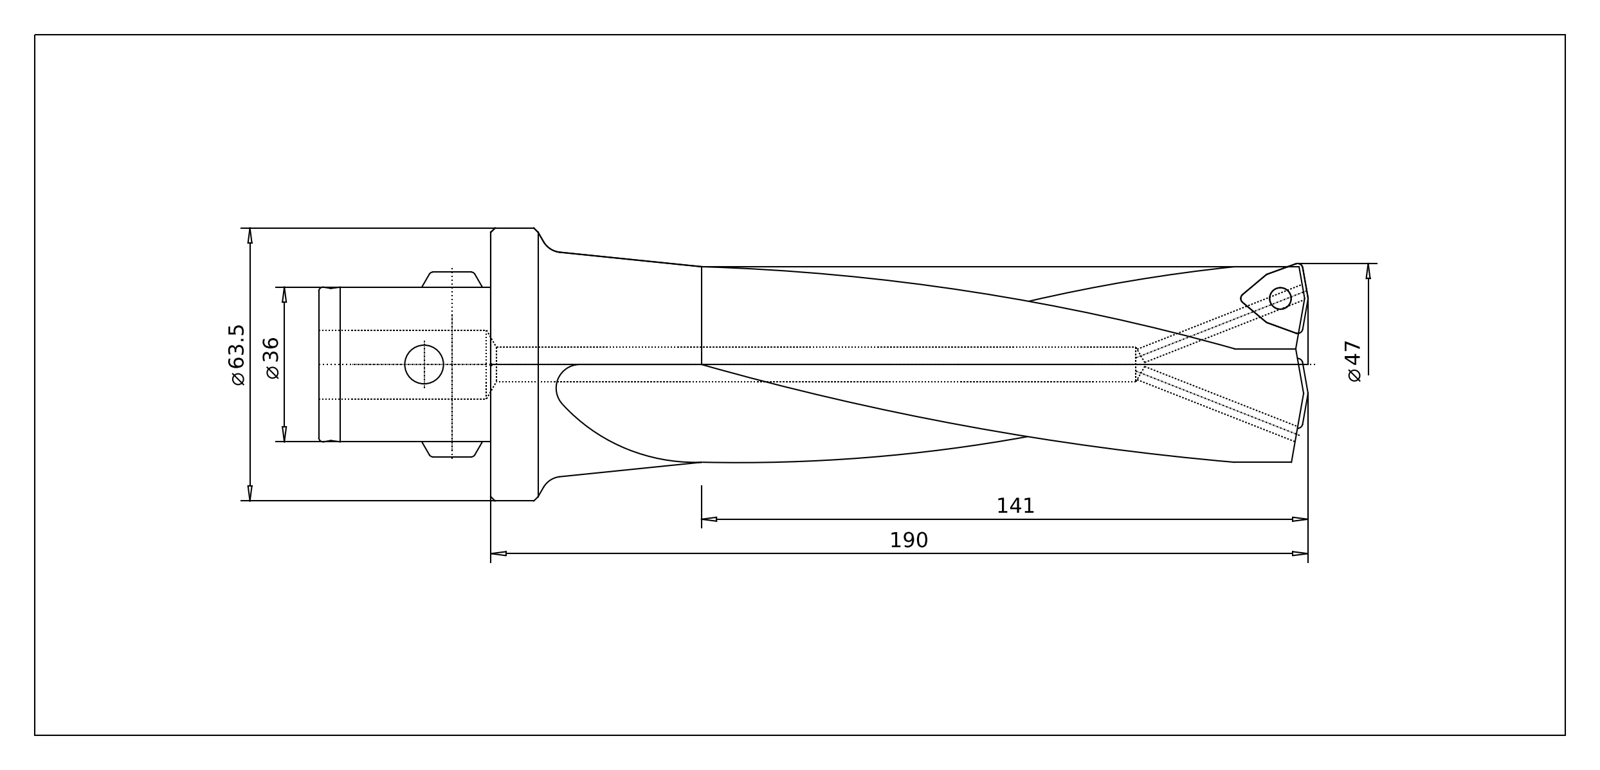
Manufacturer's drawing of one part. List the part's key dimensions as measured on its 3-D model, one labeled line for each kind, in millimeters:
Part name (STEP PRODUCT): 336.747 Kaiser WB 47-141 X CK6|694.143 Kaiser ETL M4 X 11,8 T15 IP 10S_Standard;NONE; 336.747 Kaiser WB 47-141 X CK6|336.747 Kaiser WB 47-141 X CK6_Standard-2;NONE; 336.747 Kaiser WB 47-141 X CK6|336.747 Kaiser WB 47-141 X CK6_Standard-1;NONE; 336.747 Kaiser WB 47-141 X CK6|336.747 Kaiser WB 47-141 X CK6_Standard;NONE (+2 more)
STEP written by: ACIS (automotive_design)
Units: millimetres
Bodies: 7 solids, 371 faces (83 planar, 115 cylindrical, 173 other)
Overall size (bounding box): 230 × 63.5 × 63.5
Volume: 253 096 mm³ · Surface area: 49 664 mm²
Round holes (diameter × count): ⌀3.1 ×2, ⌀3.35 ×2, ⌀4 ×2, ⌀4.4 ×2, ⌀5 ×1, ⌀9 ×1, ⌀14 ×1, ⌀16 ×1, ⌀18.5 ×1
Round bosses / shafts (diameter × count): ⌀5.5 ×2, ⌀63.5 ×1, ⌀45.48 ×1, ⌀36 ×1, ⌀13.93 ×1, ⌀10 ×1
Partial cylindrical surfaces — rounded edges, fillets, slot ends (radius × count): R0.25 ×12, R0.6 ×12, R0.2 ×10, R2.1 ×4, R1.3 ×1, R1.82 ×1
Main face-to-face distances: 40, 4.76, 5.11, 9.87, 3.84, 0.35, 11.98, 51.98, 4.5, 5.37
Hole centre spacings: 22.12, 198.91, 199.16, 199.39, 199.64
